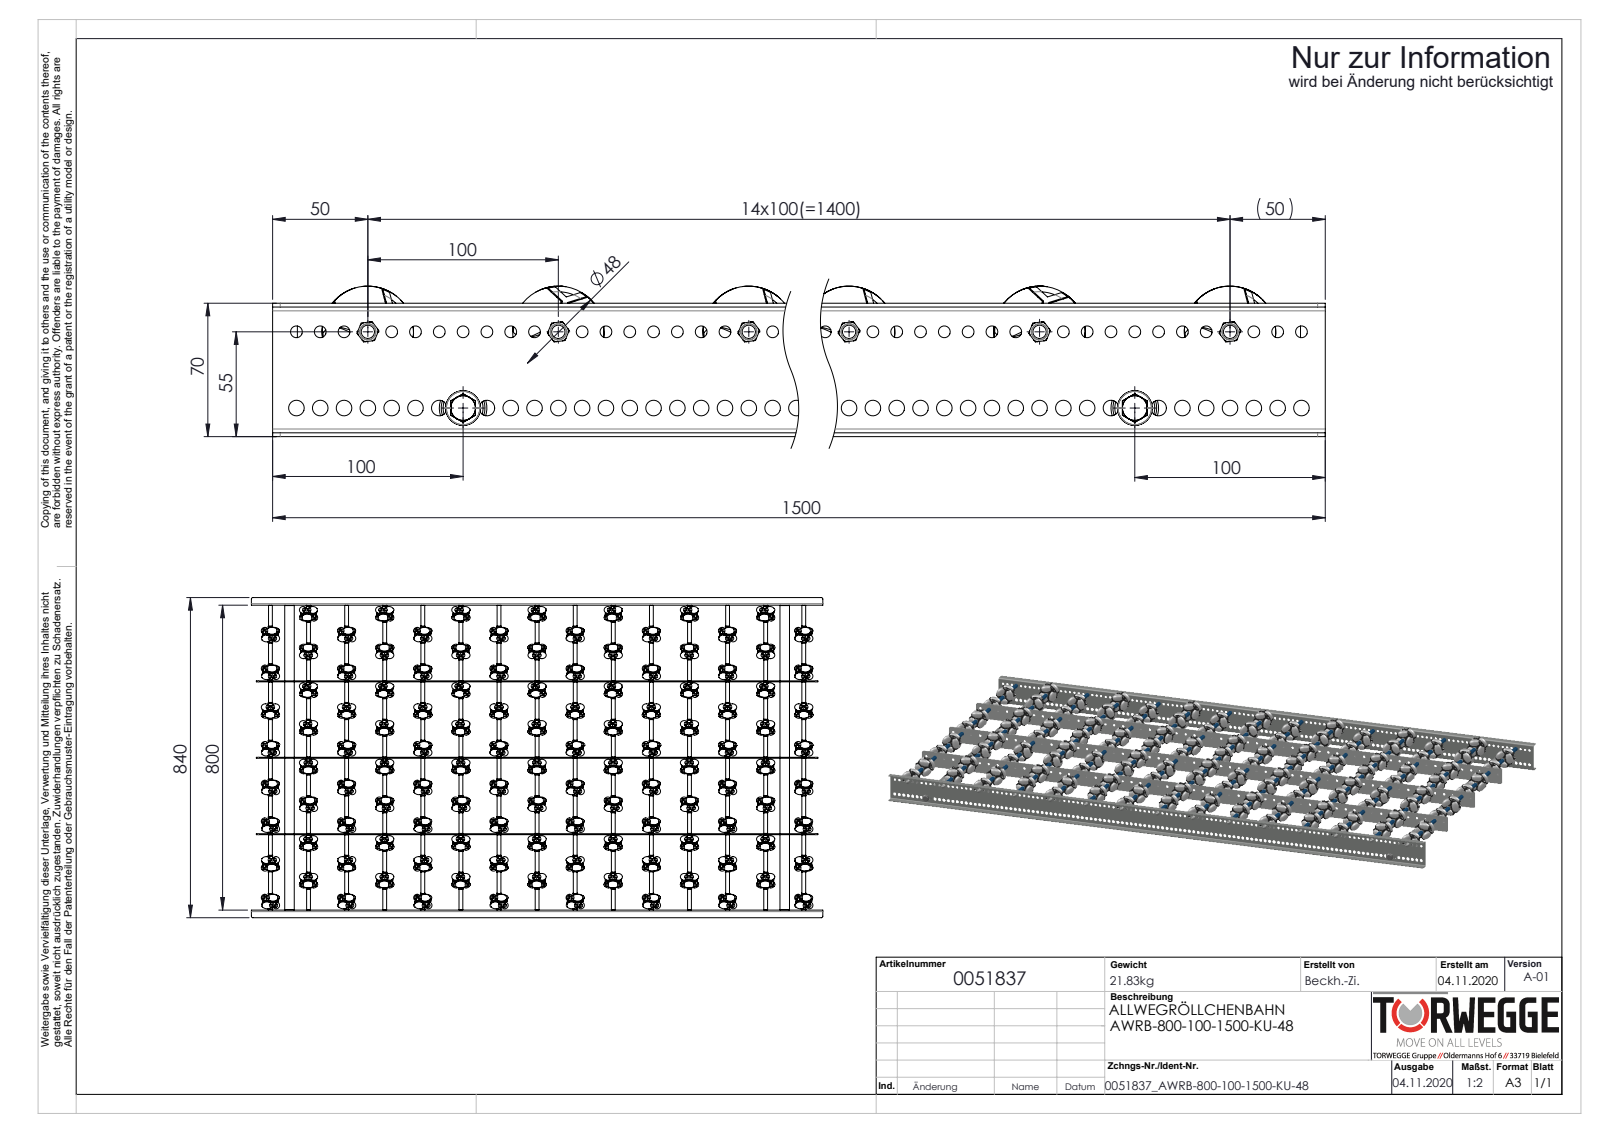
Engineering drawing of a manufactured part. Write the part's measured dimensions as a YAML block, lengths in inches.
part_name: "Traversen_KFG_L800; 0027528_BUCHSE-HOHLNIETE ZU AWR48; Profil-RB-20x70x20x2_S100216_U-PROFIL-20-70-20-2-RB-L=1500; 0019730_Tragrollenrohr-Ø10x1,75KU_KFG_0019730_L=54 (+8 more)"
step_written_by: "SolidWorks 2020 (AUTOMOTIVE_DESIGN)"
units: inches
bodies: {solids: 1980, faces: 35246, planar: 12168, cylindrical: 14004, other: 9074}
overall_size: [59.055, 33.071, 3.11]
volume: 429.4
surface_area: 7542
round_holes:
  - {diameter: 0.146, count: 720}
  - {diameter: 0.165, count: 720}
  - {diameter: 0.244, count: 119}
  - {diameter: 0.323, count: 119}
  - {diameter: 0.256, count: 59}
  - {diameter: 0.194, count: 15}
  - {diameter: 0.331, count: 15}
  - {diameter: 0.268, count: 2}
  - {diameter: 0.827, count: 2}
round_bosses_or_shafts:
  - {diameter: 0.157, count: 720}
  - {diameter: 0.146, count: 629}
  - {diameter: 0.315, count: 17}
  - {diameter: 1.854, count: 15}
  - {diameter: 1.654, count: 15}
  - {diameter: 0.433, count: 15}
  - {diameter: 0.394, count: 15}
  - {diameter: 0.276, count: 15}
partial_cylinders:
  - {radius: 0.157, count: 8}
  - {radius: 0.079, count: 4}
  - {radius: 0.197, count: 4}
face_to_face_distances: [0.079, 7.894, 0.098, 31.575, 15.787, 7.795, 7.992, 2.677, 31.496, 31.654]
hole_center_spacings: [1.42, 1.419, 3.898, 1.42, 4.831, 1.419, 3.327, 4.377]
